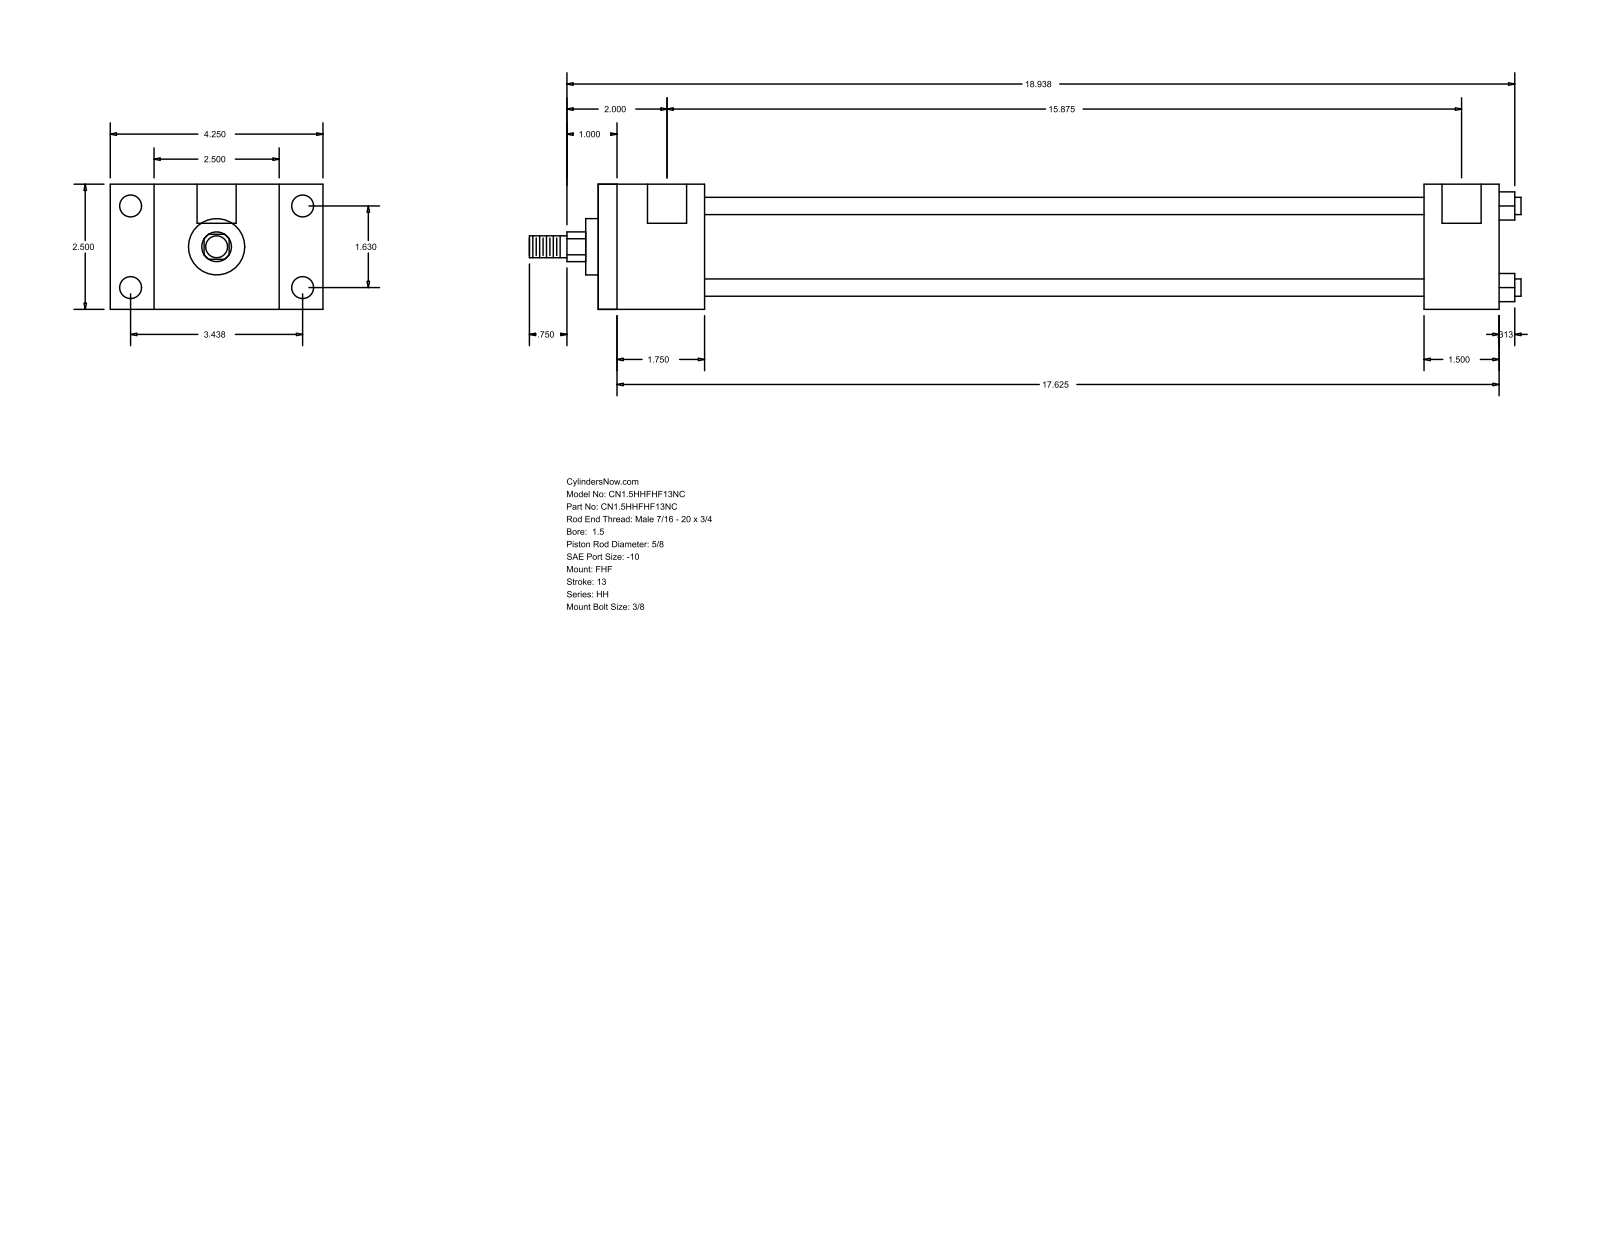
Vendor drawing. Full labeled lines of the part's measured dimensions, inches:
Part name (STEP PRODUCT): HH_FHF__0150_0.625
STEP written by: GSSL Pune (CONFIG_CONTROL_DESIGN)
Units: inches
Bodies: 0 solids, 88 faces (60 planar, 28 cylindrical, 0 other)
Overall size (bounding box): 19.813 × 4.25 × 2.5
Round holes (diameter × count): ⌀0.219 ×4, ⌀0.438 ×4, ⌀0.781 ×2
Round bosses / shafts (diameter × count): ⌀0.345 ×4, ⌀1.75 ×1, ⌀1.125 ×1, ⌀0.625 ×1, ⌀0.437 ×1
Partial cylindrical surfaces — rounded edges, fillets, slot ends (radius × count): R0.297 ×1
Main face-to-face distances: 2.5, 0.875, 3.375, 2.125, 4.25, 18, 15.875, 16.5, 14.375, 1.5
Hole centre spacings: 0.063, 1.63, 3.438, 3.805, 15.937, 16, 15.875
